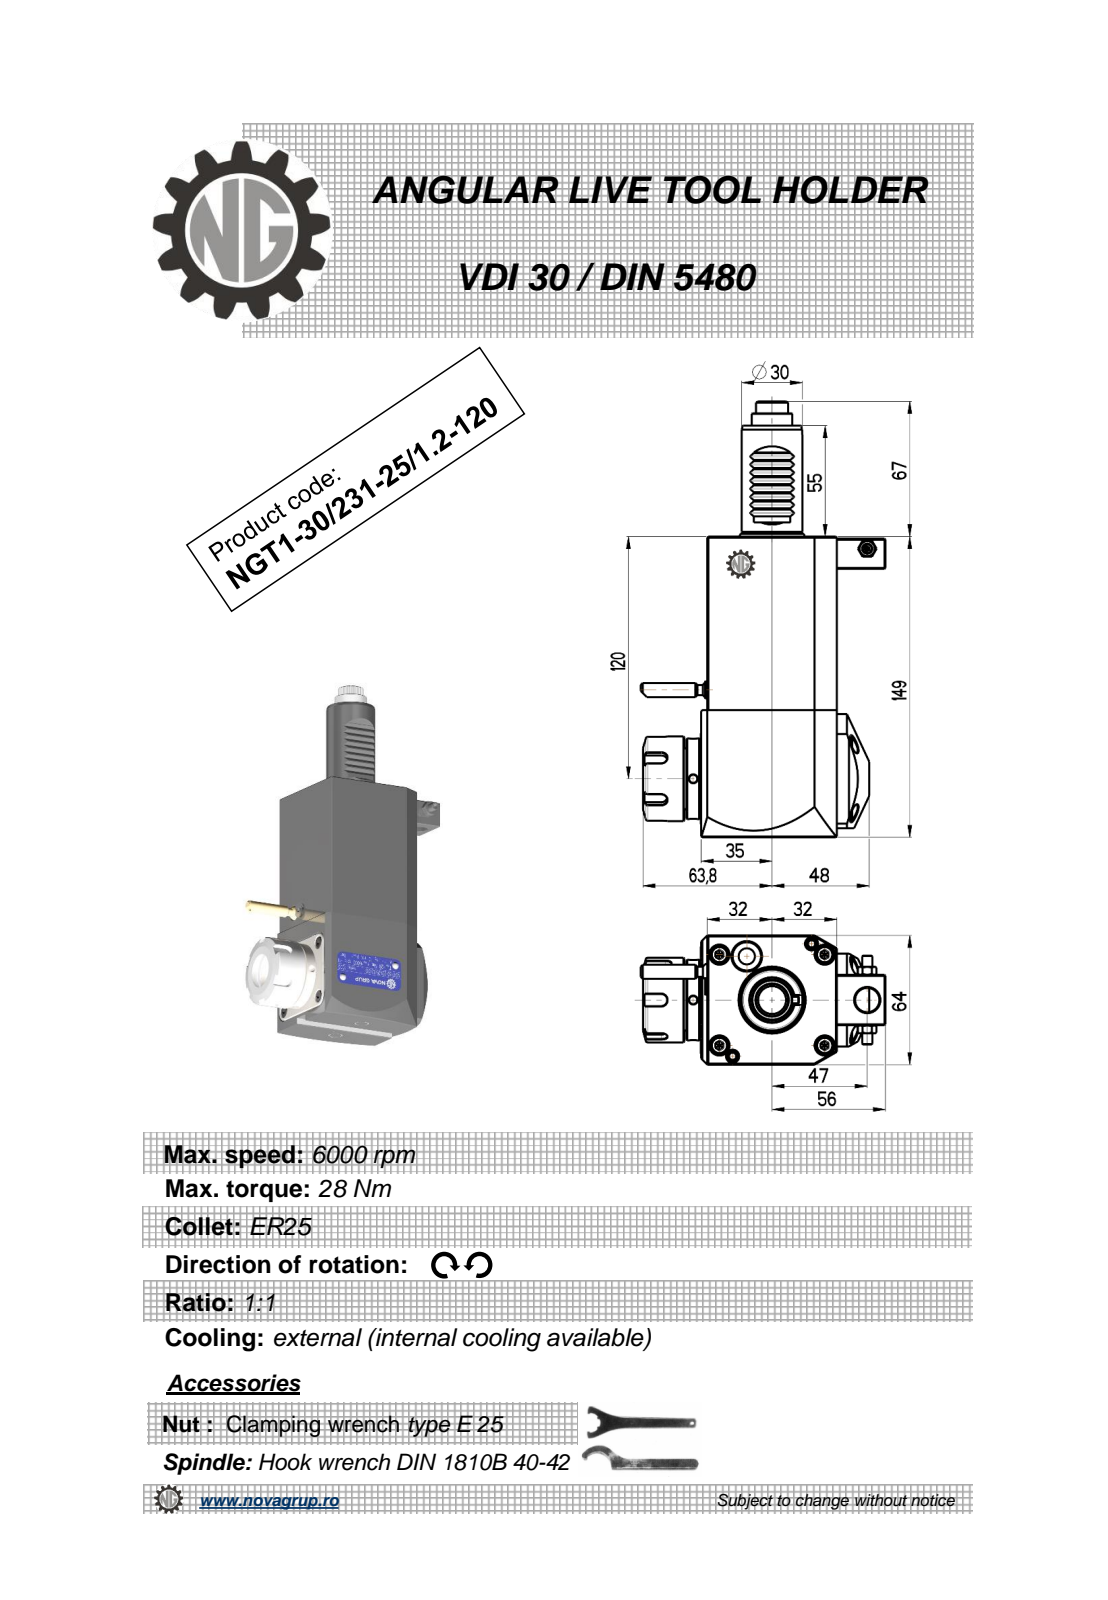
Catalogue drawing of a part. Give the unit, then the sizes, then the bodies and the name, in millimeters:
Units: millimetres
Overall size (bounding box): 216 × 120.88 × 64
Round holes (diameter × count): ⌀4 ×2, ⌀2.5 ×1, ⌀3 ×1, ⌀4.2 ×1, ⌀9.5 ×1, ⌀12 ×1, ⌀20.3 ×1
Round bosses / shafts (diameter × count): ⌀8.96 ×2, ⌀5 ×2, ⌀42 ×1, ⌀40 ×1, ⌀33 ×1, ⌀30 ×1, ⌀20 ×1, ⌀7 ×1
Partial cylindrical surfaces — rounded edges, fillets, slot ends (radius × count): R1.98 ×36, R0.26 ×12, R0.3 ×8, R3 ×5, R160 ×2, R7.08 ×1, R7.92 ×1, R13 ×1
Main face-to-face distances: 64, 149, 3.2, 67.2, 67, 3, 0.5, 55, 16, 4
Hole centre spacings: 46.17, 68.94, 85.95, 111.5, 142.77
Volume: 717 034 mm³ · Surface area: 63 291 mm²
Bodies: 1 solid, 493 faces (184 planar, 157 cylindrical, 152 other)
Part name (STEP PRODUCT): NGT1_30_231_25_1_2_120
STEP written by: PRO/ENGINEER BY PARAMETRIC TECHNOLOGY CORPORATION, 2010280 (CONFIG_CONTROL_DESIGN)
